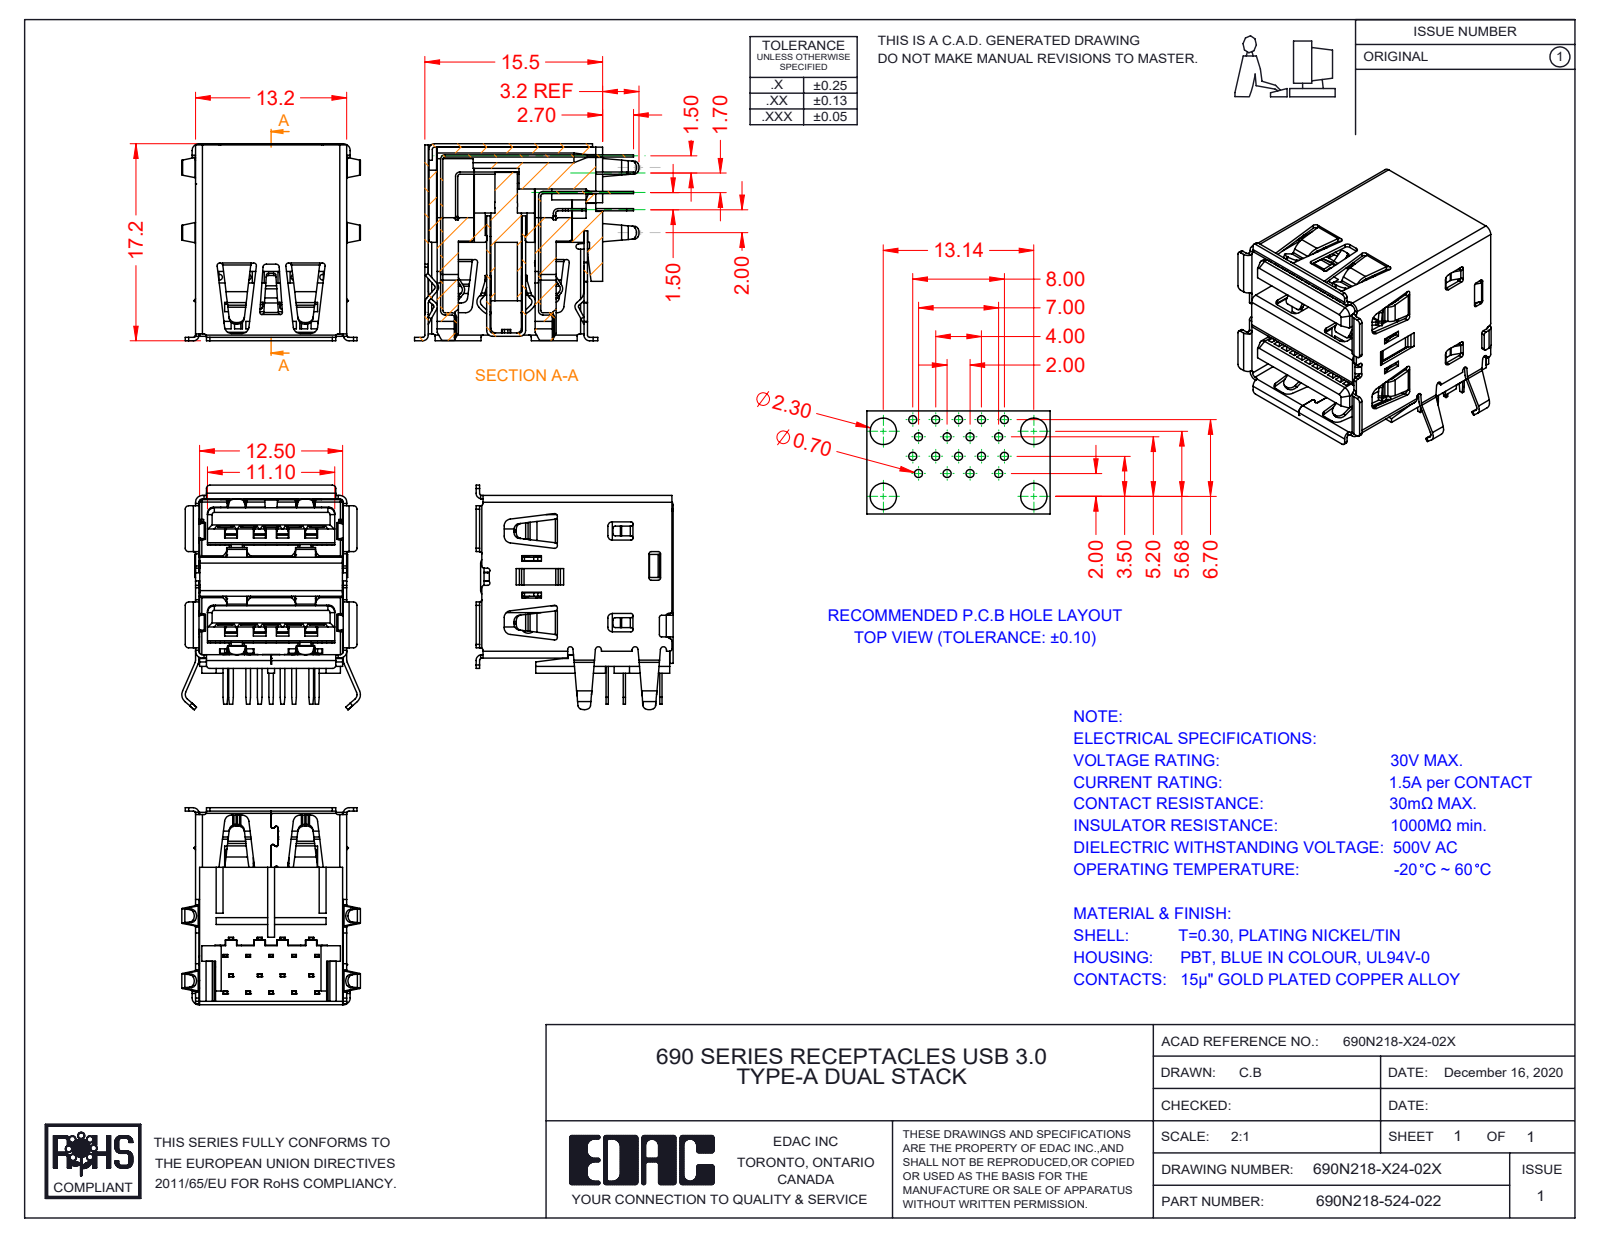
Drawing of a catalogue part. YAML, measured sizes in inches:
part_name: "Contact 7 690N218-X24-02X; Insulator2 690N218-X24-02X_Blue; Contact 18 690N218-X24-02X; Contact 9 690N218-X24-02X (+8 more)"
step_written_by: "SolidWorks 2020 (AUTOMOTIVE_DESIGN)"
units: inches
bodies: {solids: 25, faces: 3066, planar: 2258, cylindrical: 788, other: 20}
overall_size: [0.772, 0.677, 0.614]
volume: 0.104
surface_area: 11.44
round_holes:
  - {diameter: 0.02, count: 5}
partial_cylinders:
  - {radius: 0.008, count: 90}
  - {radius: 0.02, count: 72}
  - {radius: 0.012, count: 54}
  - {radius: 0.006, count: 50}
  - {radius: 0.016, count: 39}
  - {radius: 0.024, count: 34}
  - {radius: 0.004, count: 30}
  - {radius: 0.039, count: 20}
face_to_face_distances: [0.02, 0.508, 0.053, 0.067, 0.213, 0.335, 0.033, 0.028, 0.031, 0.014]
hole_center_spacings: [0.079, 0.098, 0.177, 0.256, 0.157, 0.354]
